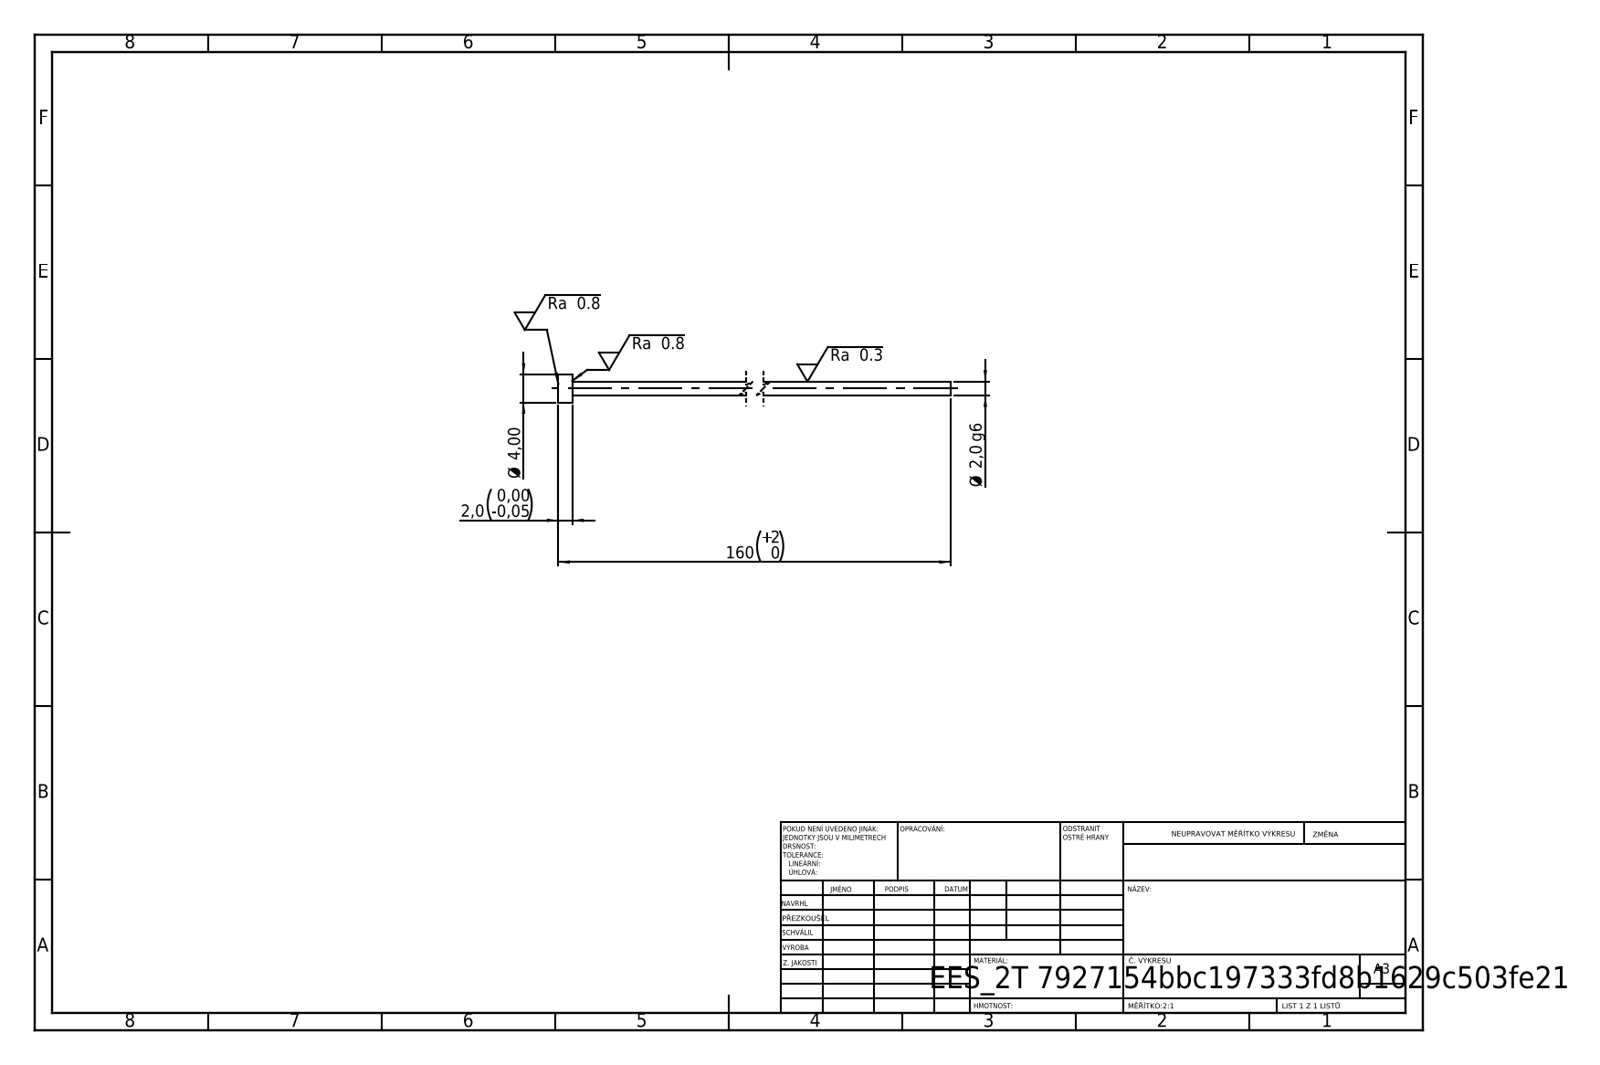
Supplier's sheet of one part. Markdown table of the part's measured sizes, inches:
| quantity | value |
| --- | --- |
| STEP written by | SolidWorks 2019 (CONFIG_CONTROL_DESIGN) |
| units | inches |
| bodies | 1 solid, 7 faces (3 planar, 4 cylindrical, 0 other) |
| overall size | 6.299 × 0.157 × 0.157 |
| volume | 0.032 in³ |
| surface area | 1.617 in² |
| round bosses / shafts (diameter × count) | 0.157 × 1, 0.079 × 1 |
| main face-to-face distances | 0.079, 6.299, 6.22 |
